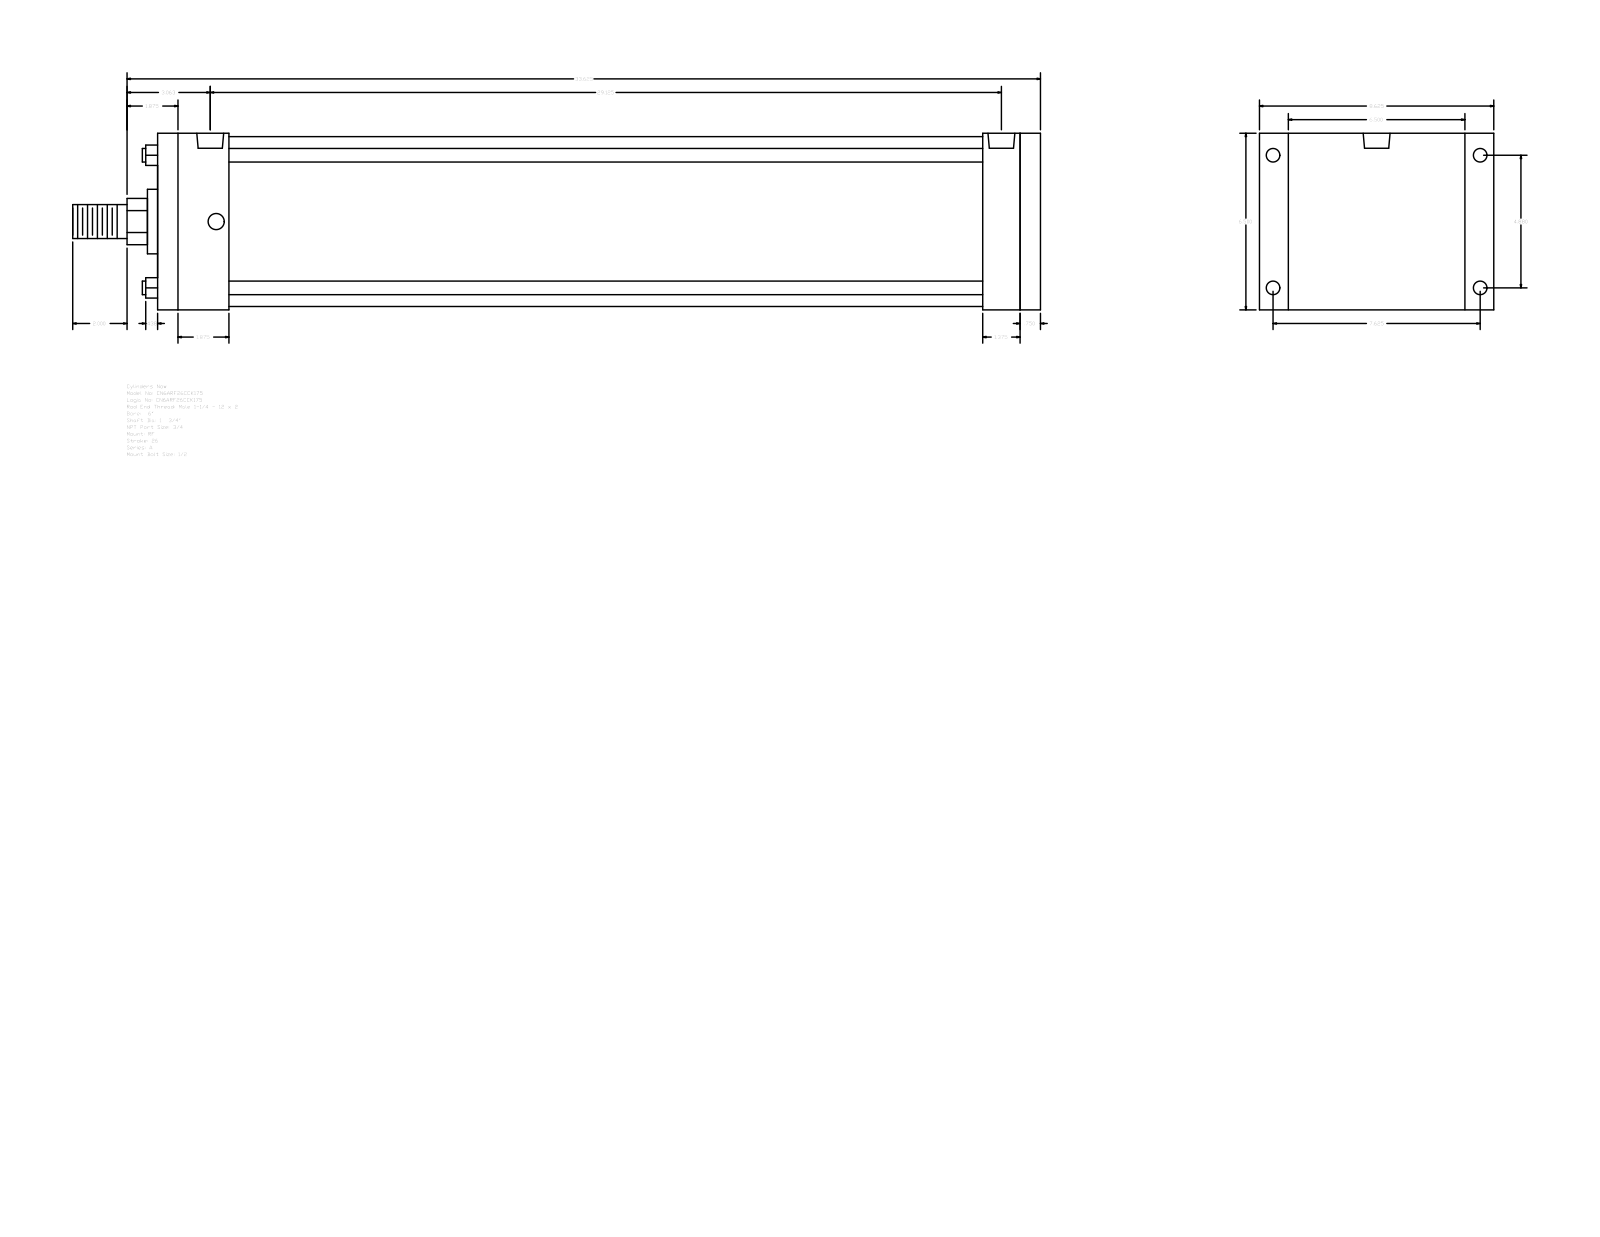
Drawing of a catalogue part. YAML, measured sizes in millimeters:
part_name: "A_RF__0600_1.75"
step_written_by: "GSSL Pune (CONFIG_CONTROL_DESIGN)"
units: millimeters
bodies: {solids: 0, faces: 92, planar: 64, cylindrical: 28, other: 0}
overall_size: [904.88, 219.07, 165.1]
round_holes:
  - {diameter: 12.7, count: 4}
  - {diameter: 15.08, count: 4}
  - {diameter: 25.12, count: 2}
round_bosses_or_shafts:
  - {diameter: 12.7, count: 4}
  - {diameter: 158.75, count: 1}
  - {diameter: 60.33, count: 1}
  - {diameter: 44.45, count: 1}
  - {diameter: 31.75, count: 1}
partial_cylinders:
  - {radius: 21.63, count: 1}
face_to_face_distances: [165.1, 825.51, 806.45, 19.06, 66.68, 739.77, 758.83, 771.53, 704.85, 34.92]
hole_center_spacings: [5.56, 123.96, 193.68, 229.95, 728.65, 734.21, 739.77]
